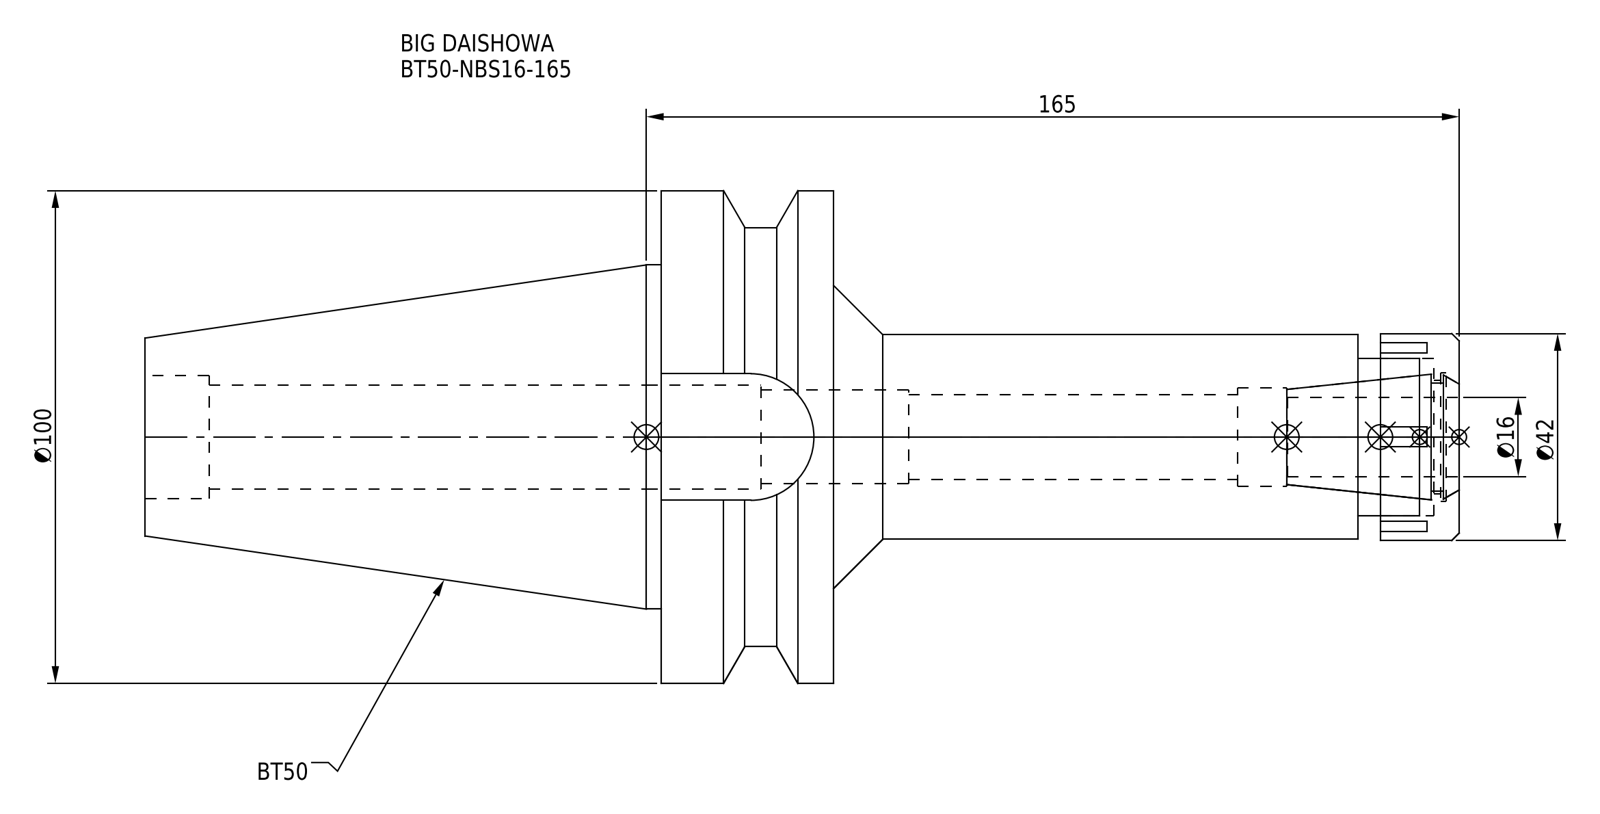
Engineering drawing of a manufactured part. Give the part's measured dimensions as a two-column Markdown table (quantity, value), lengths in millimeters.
| quantity | value |
| --- | --- |
| part name | BT50-NBS16-165.stp; DXF_TEMP_ASSY_ASM_4_ASM.stp; BT50-NBS16-165; BT50NB16165-160_ASM.stp (+3 more) |
| STEP written by | SolidWorks 2019 (CONFIG_CONTROL_DESIGN) |
| units | millimeters |
| bodies | 2 solids, 93 faces (45 planar, 34 cylindrical, 14 other) |
| overall size | 266.8 × 100 × 100 |
| volume | 582 443 mm³ |
| surface area | 81 374 mm² |
| round holes (diameter × count) | 17.3 × 1, 19 × 1, 20 × 1, 21.2 × 1, 23 × 1, 25 × 1, 26 × 1, 32 × 1 |
| round bosses / shafts (diameter × count) | 100 × 1, 85 × 1, 69.85 × 1, 42 × 1, 41.5 × 1 |
| partial cylindrical surfaces (radius × count) | 12.85 × 1 |
| main face-to-face distances | 35, 127, 162, 266.8, 139.8, 104.8, 70.8, 8, 20.5, 106.5 |
